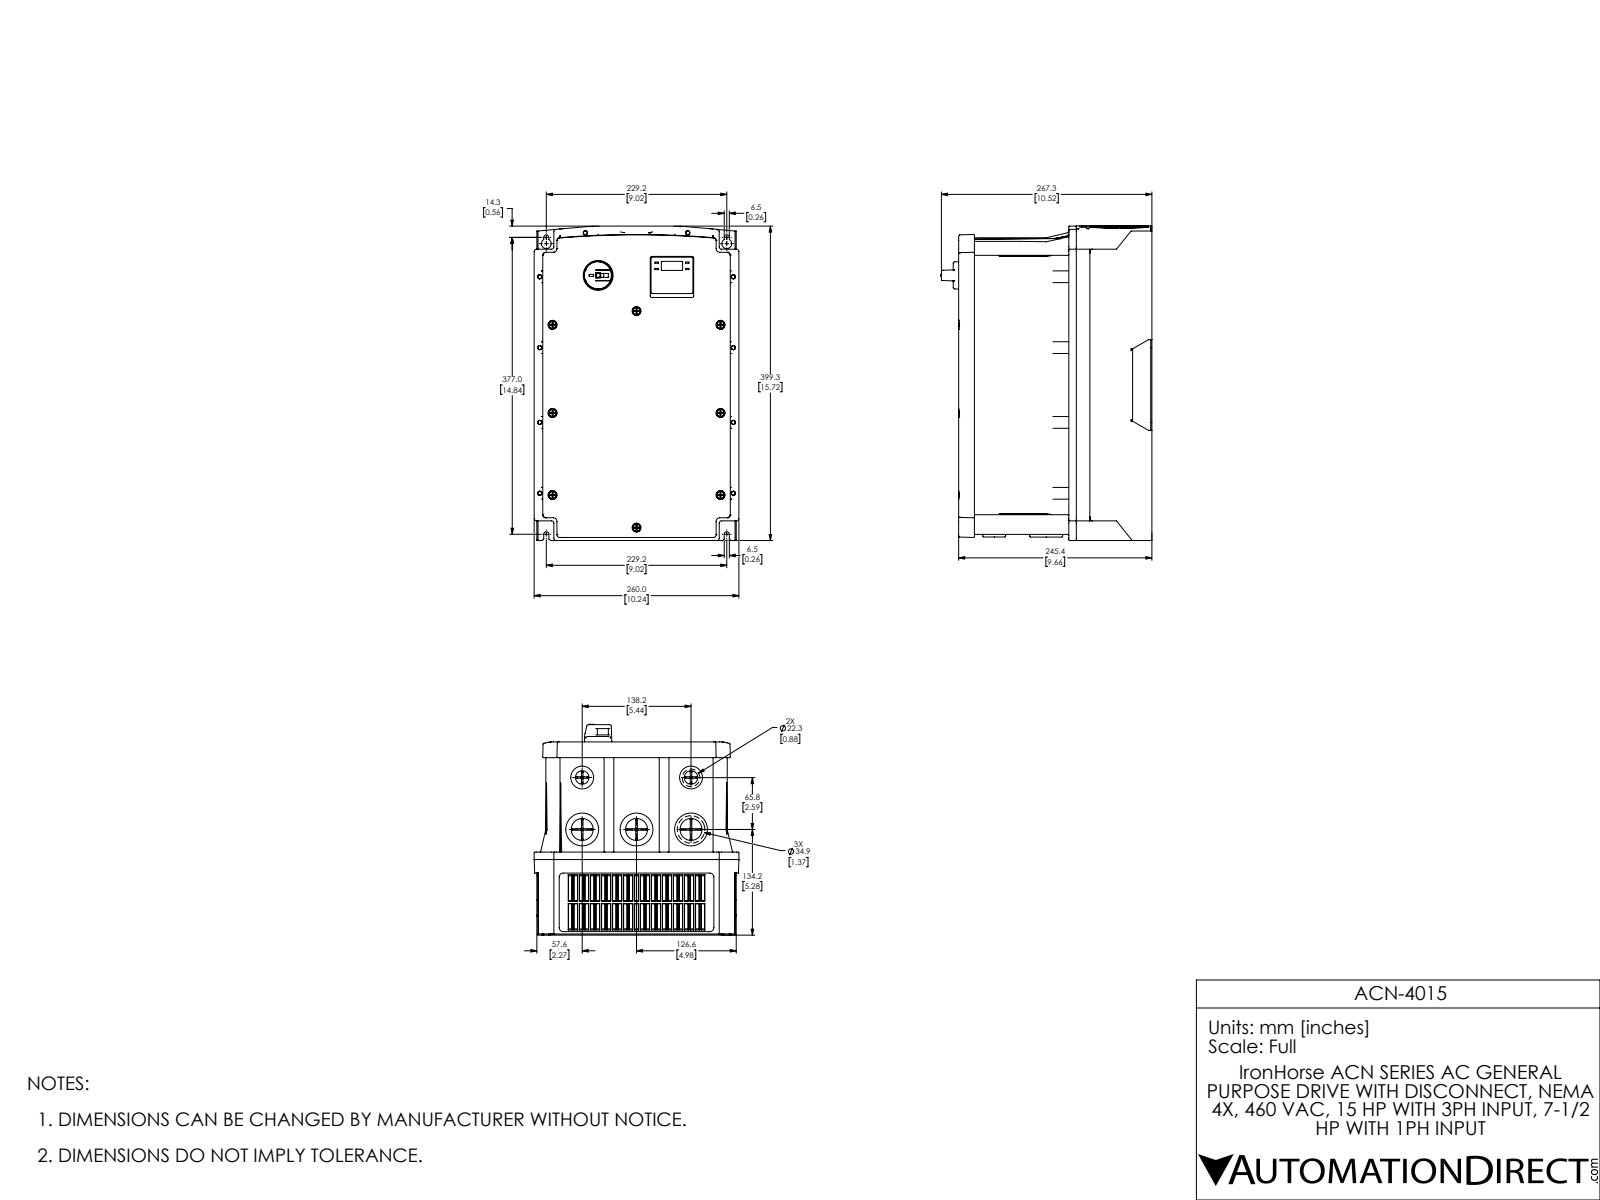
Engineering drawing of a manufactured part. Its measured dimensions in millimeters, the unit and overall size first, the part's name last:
Units: millimetres
Overall size (bounding box): 399.6 × 267.8 × 260
Round holes (diameter × count): ⌀5 ×12, ⌀5.5 ×12, ⌀10.4 ×8, ⌀27.9 ×3, ⌀38.7 ×3, ⌀12.5 ×2, ⌀17.2 ×2, ⌀22.3 ×2, ⌀26 ×2, ⌀30 ×2, ⌀45 ×2, ⌀60 ×2
Round bosses / shafts (diameter × count): ⌀10 ×8, ⌀41.7 ×3, ⌀34.3 ×3, ⌀65 ×2, ⌀50 ×2, ⌀35 ×2, ⌀29 ×2, ⌀21.6 ×2
Partial cylindrical surfaces — rounded edges, fillets, slot ends (radius × count): R1 ×127, R0.3 ×115, R0.5 ×97, R0.2 ×61, R0.8 ×36, R3 ×34, R5 ×25, R4 ×20
Main face-to-face distances: 1.5, 245.4, 240.3, 11.4, 241.8, 251.7, 9.9, 243.9, 230.4, 250.2
Hole centre spacings: 90, 103.31, 130.5, 185, 246, 261.95, 307.8, 213.2
Volume: 21 690 000 mm³ · Surface area: 892 684 mm²
Bodies: 2 solids, 5356 faces (2408 planar, 1422 cylindrical, 1526 other)
Part name (STEP PRODUCT): total_s100_ip66_110_150_v3_asm red 1ext RED2 NEW1b2 COMPLETE EXT2F2 fill WITH LOTO KNOB sm2 cmb r1
STEP written by: SolidWorks 2017 (AUTOMOTIVE_DESIGN)
